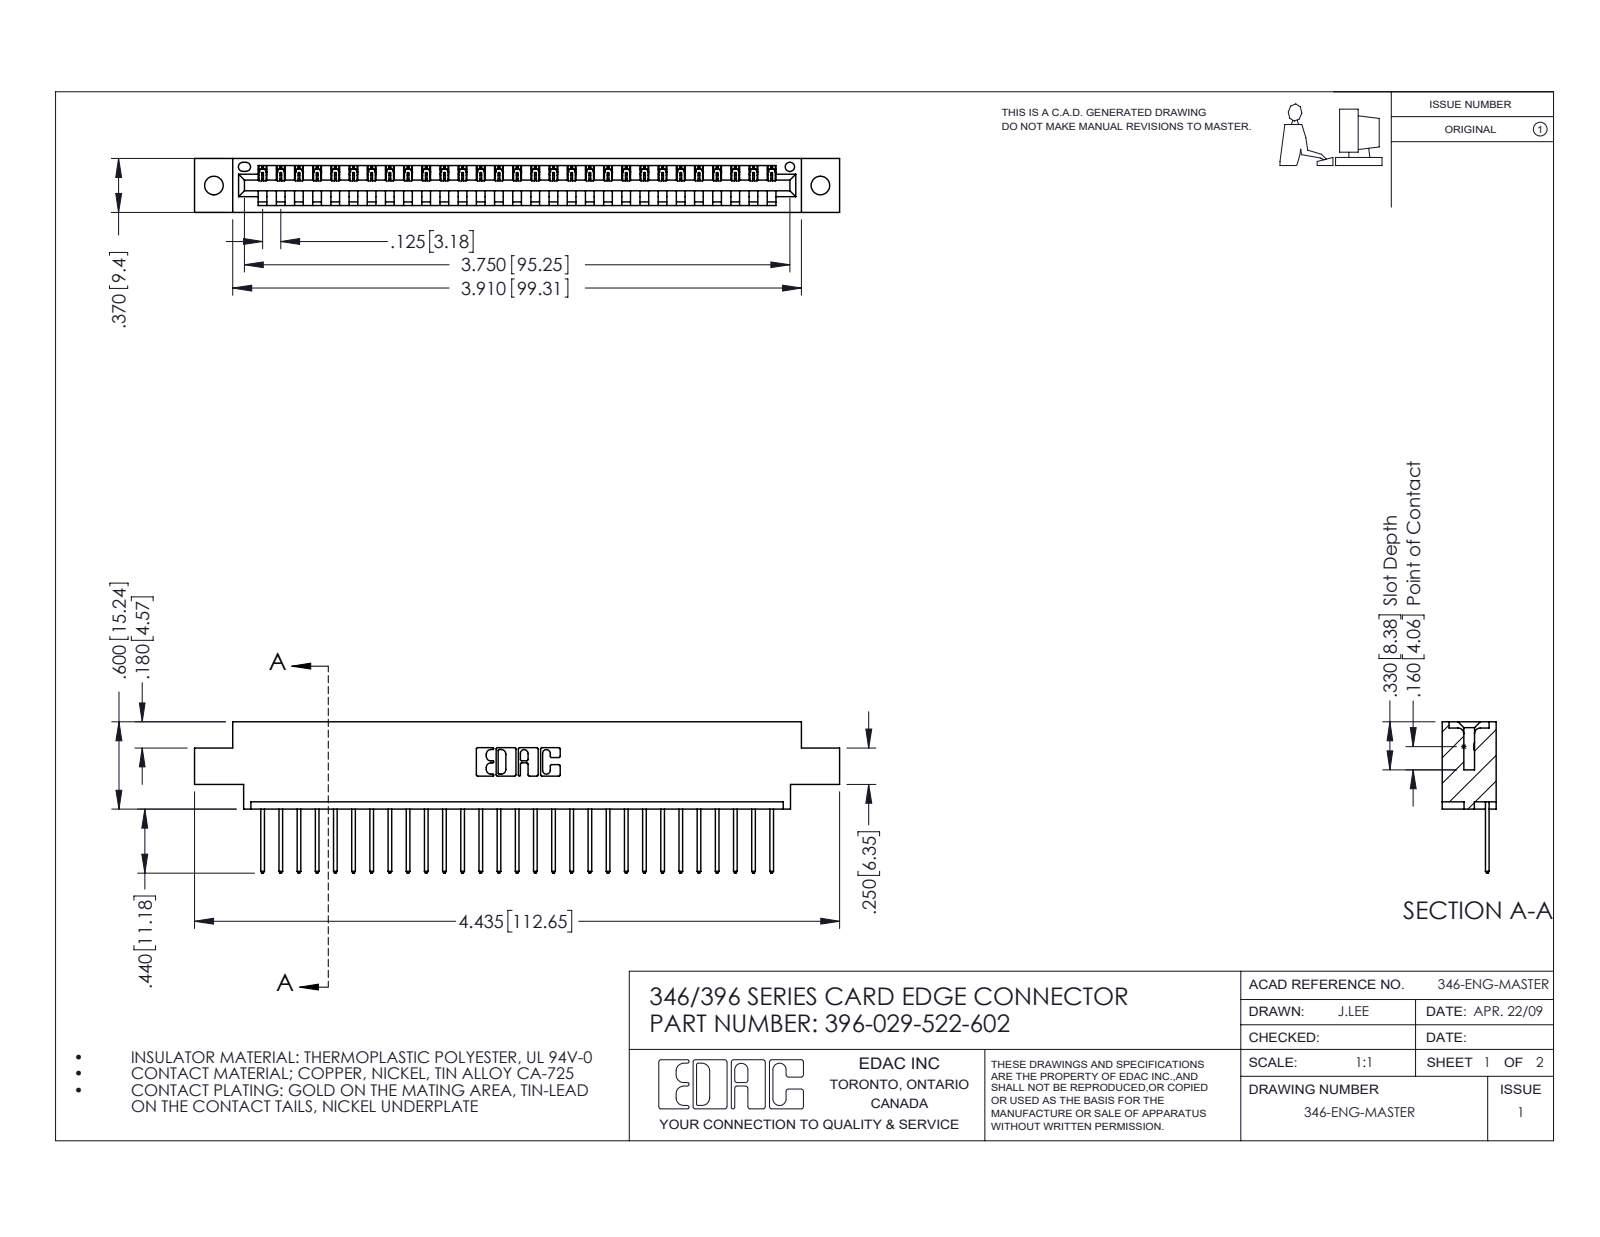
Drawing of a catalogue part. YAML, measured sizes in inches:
part_name: "396-029-522-602; 345-292-001_345-293-122; 346 Part_0.170 Offset - 0.128 Dia"
step_written_by: "SolidWorks 2016 (CONFIG_CONTROL_DESIGN)"
units: inches
bodies: {solids: 30, faces: 1808, planar: 1240, cylindrical: 568, other: 0}
overall_size: [4.435, 1.04, 0.37]
volume: 0.641
surface_area: 20.13
round_holes:
  - {diameter: 0.128, count: 2}
  - {diameter: 0.064, count: 1}
partial_cylinders:
  - {radius: 0.006, count: 58}
  - {radius: 0.01, count: 58}
  - {radius: 0.01, count: 22}
  - {radius: 0.007, count: 6}
  - {radius: 0.031, count: 6}
  - {radius: 0.026, count: 3}
  - {radius: 0.031, count: 2}
  - {radius: 0.04, count: 2}
face_to_face_distances: [0.048, 0.322, 0.37, 0.25, 0.072, 0.298, 0.025, 0.148, 0.222, 0.1]
hole_center_spacings: [0.246, 3.962, 4.17]
